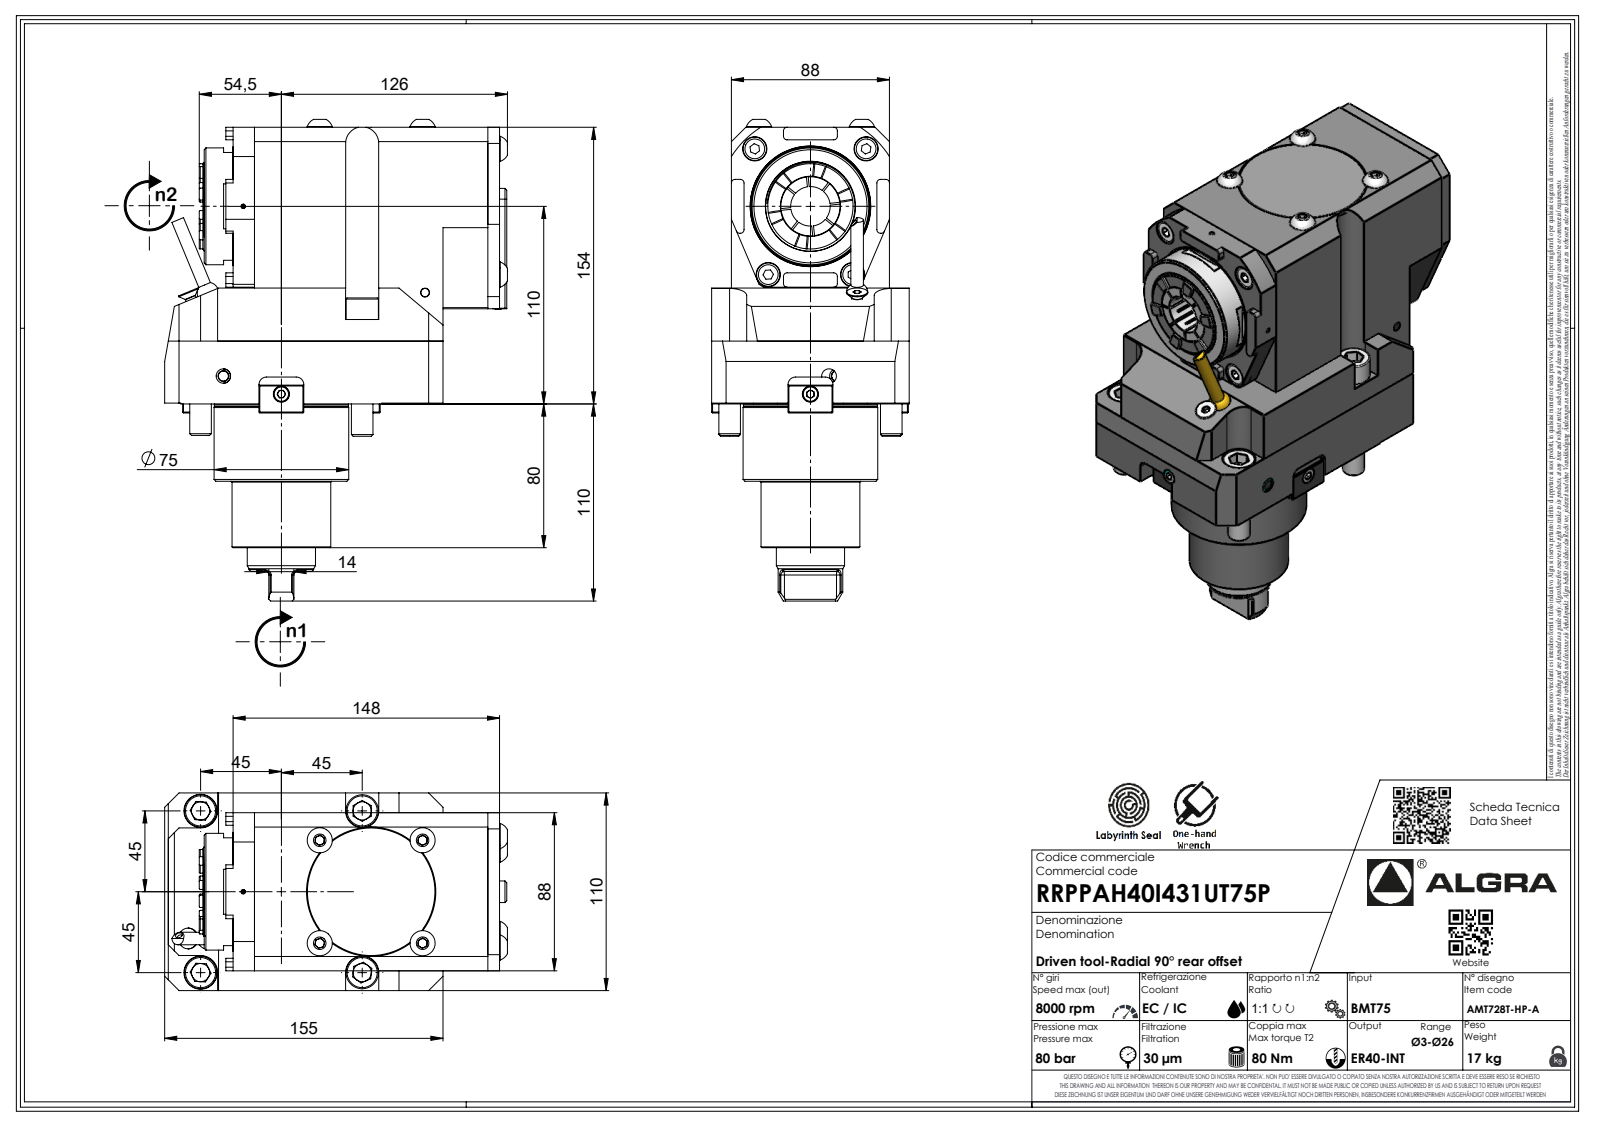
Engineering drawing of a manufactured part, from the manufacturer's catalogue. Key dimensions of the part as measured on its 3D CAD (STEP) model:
Part name (STEP PRODUCT): RRPPAH40I431UT75P
STEP written by: SolidWorks 2023 (AUTOMOTIVE_DESIGN)
Units: millimetres
Bodies: 1 solid, 640 faces (446 planar, 84 cylindrical, 110 other)
Overall size (bounding box): 268.1 × 190.9 × 110
Volume: 2 540 000 mm³ · Surface area: 146 682 mm²
Round holes (diameter × count): ⌀2.1 ×1, ⌀4 ×1
Round bosses / shafts (diameter × count): ⌀14 ×8, ⌀12 ×4, ⌀18 ×2, ⌀75 ×1, ⌀74.6 ×1, ⌀65 ×1, ⌀55 ×1, ⌀38 ×1
Partial cylindrical surfaces — rounded edges, fillets, slot ends (radius × count): R2 ×23, R0.33 ×7, R0.52 ×7, R3.7 ×7, R1 ×2, R9.25 ×2, R9.5 ×2, R0.21 ×1
Main face-to-face distances: 11, 99, 88, 110, 154, 31.5, 0.5, 153.5, 64.5, 133
